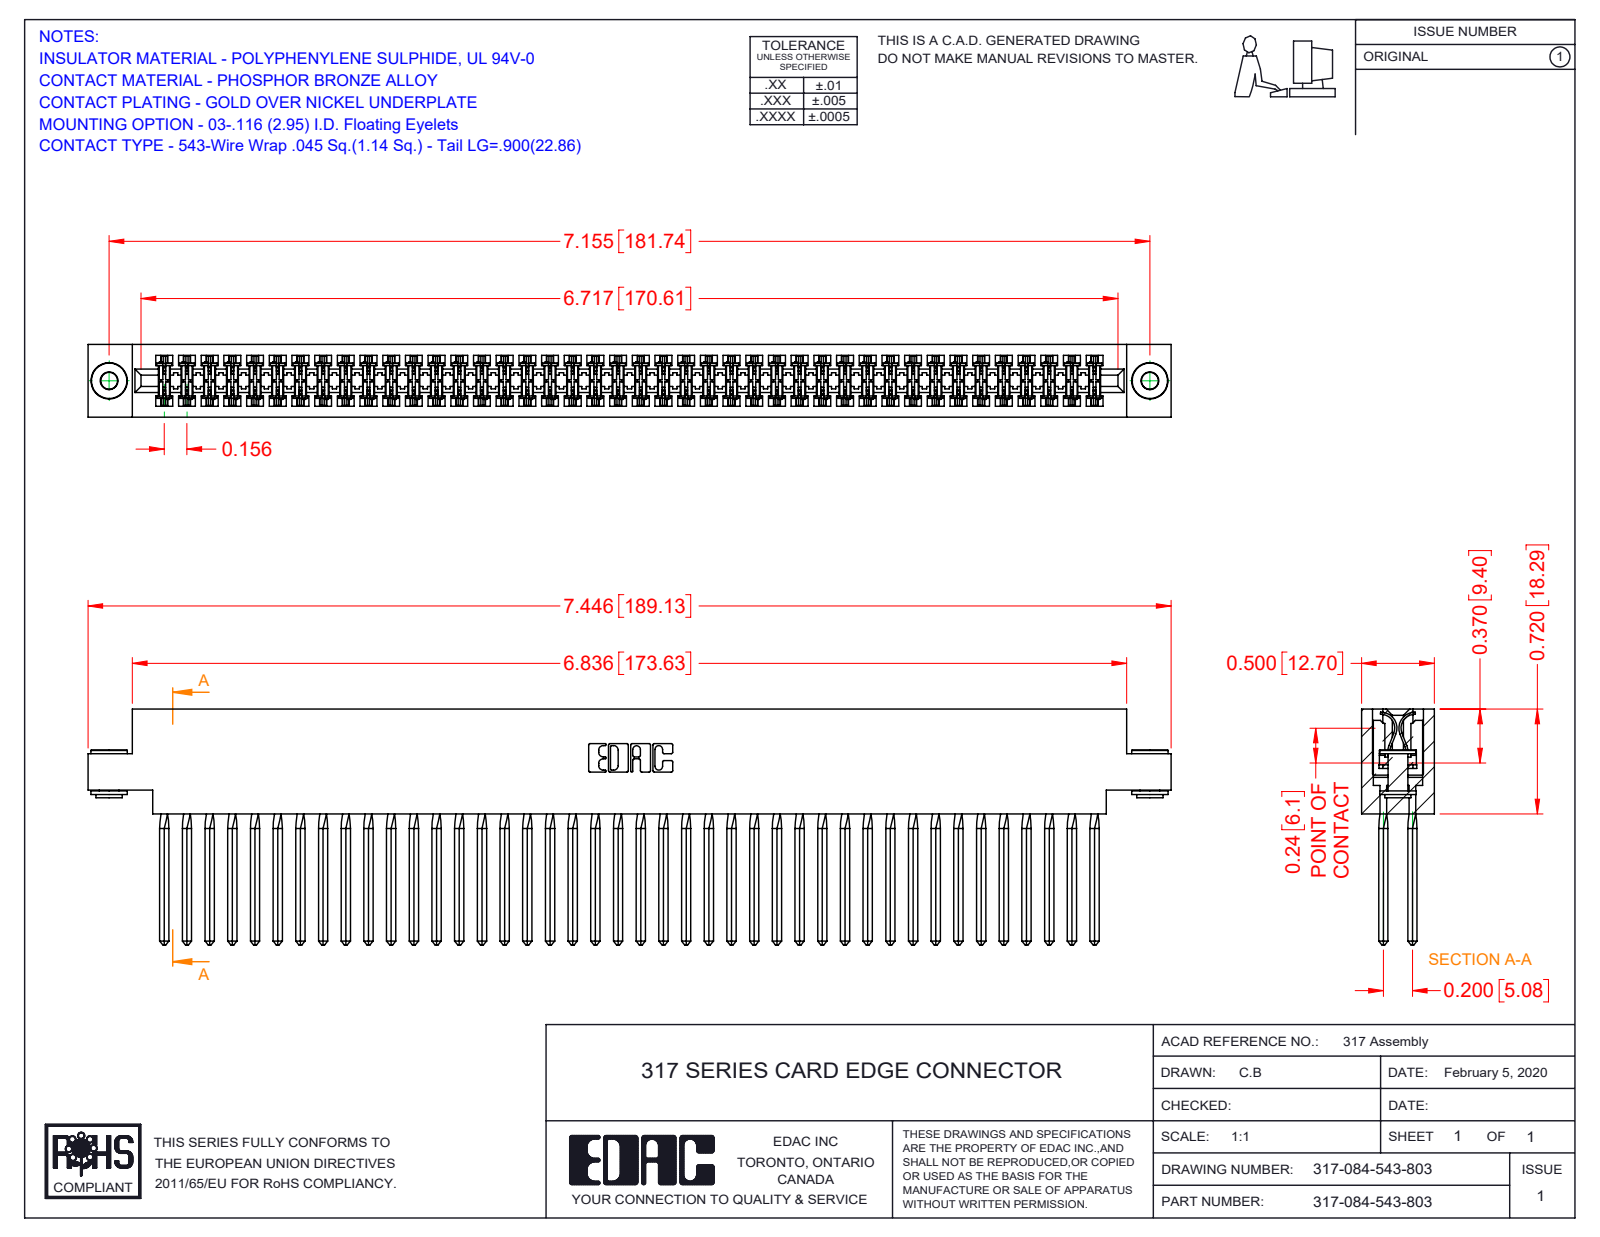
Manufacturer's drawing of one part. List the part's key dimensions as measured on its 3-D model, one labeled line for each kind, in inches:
Part name (STEP PRODUCT): 345-250-002_345-250-002-102; 317-290-001_543; 317-084-543-803; 317 Part_.156 Dia - TH
STEP written by: SolidWorks 2016 (CONFIG_CONTROL_DESIGN)
Units: inches
Bodies: 87 solids, 7616 faces (6200 planar, 1072 cylindrical, 344 other)
Overall size (bounding box): 7.446 × 1.62 × 0.5
Volume: 1.964 in³ · Surface area: 76 in²
Round holes (diameter × count): ⌀0.116 ×2, ⌀0.156 ×2
Round bosses / shafts (diameter × count): ⌀0.25 ×2, ⌀0.18 ×2, ⌀0.136 ×2
Partial cylindrical surfaces — rounded edges, fillets, slot ends (radius × count): R0.015 ×168, R0.01 ×22, R0.007 ×6, R0.031 ×6, R0.026 ×3, R0.095 ×2, R0.1 ×2, R0.11 ×2
Main face-to-face distances: 0.5, 0.075, 0.425, 0.35, 0.195, 0.11, 0.094, 0.2, 0.115, 0.131
Hole centre spacings: 7.155
